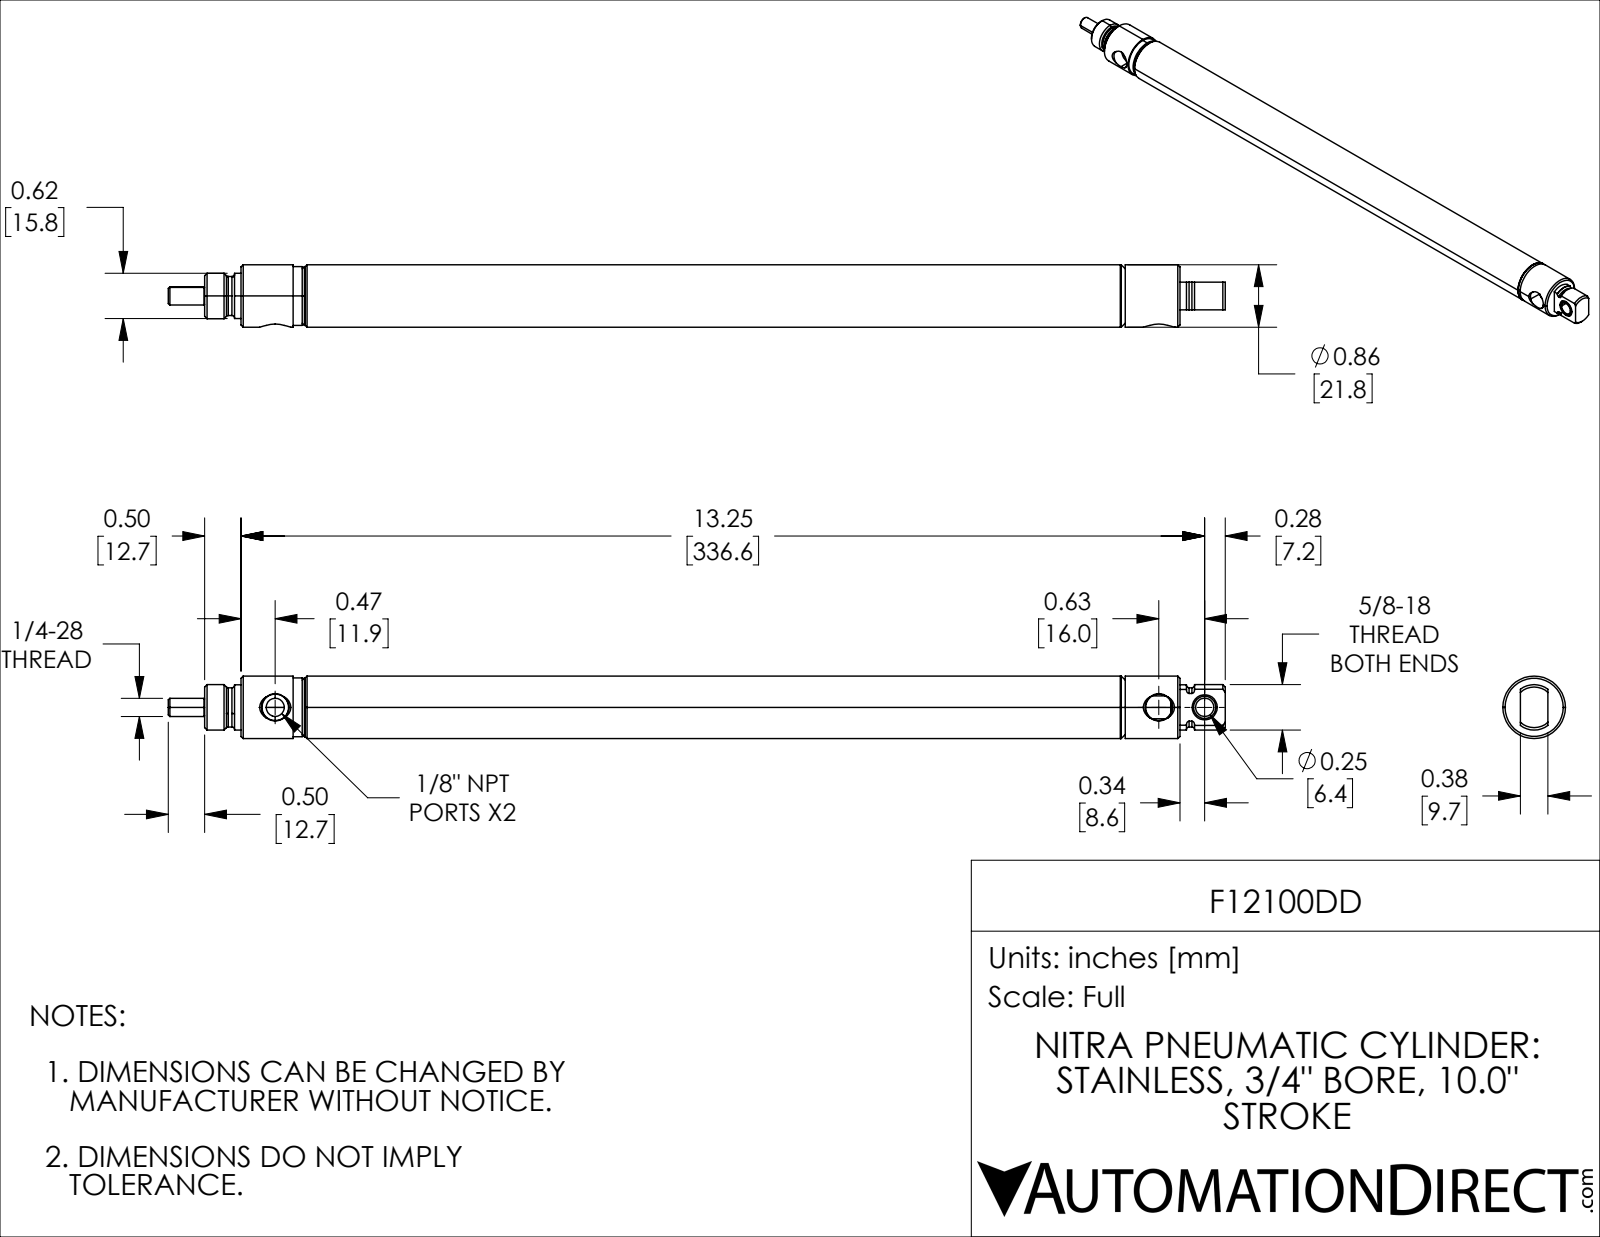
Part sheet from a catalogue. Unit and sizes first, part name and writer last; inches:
Units: inches
Overall size (bounding box): 14.532 × 0.86 × 0.86
Round holes (diameter × count): ⌀0.25 ×1, ⌀0.251 ×1, ⌀0.274 ×1, ⌀0.312 ×1, ⌀0.346 ×1, ⌀0.363 ×1, ⌀0.5 ×1, ⌀0.702 ×1
Round bosses / shafts (diameter × count): ⌀0.86 ×1, ⌀0.81 ×1, ⌀0.762 ×1, ⌀0.625 ×1, ⌀0.622 ×1, ⌀0.539 ×1, ⌀0.25 ×1, ⌀0.23 ×1
Partial cylindrical surfaces — rounded edges, fillets, slot ends (radius × count): R0.269 ×1
Main face-to-face distances: 0.844, 1.594, 12.438, 10, 10.844, 11.816, 1.816, 0.972, 0.5, 0.38
Hole centre spacings: 0.63, 12.15, 12.78
Volume: 3.526 in³ · Surface area: 84.29 in²
Bodies: 5 solids, 158 faces (29 planar, 61 cylindrical, 68 other)
Part name (STEP PRODUCT): F12100DD_7; F12100DD_9; F12100DD; F12100DD_5 (+2 more)
STEP written by: SolidWorks 2021 (CONFIG_CONTROL_DESIGN)
